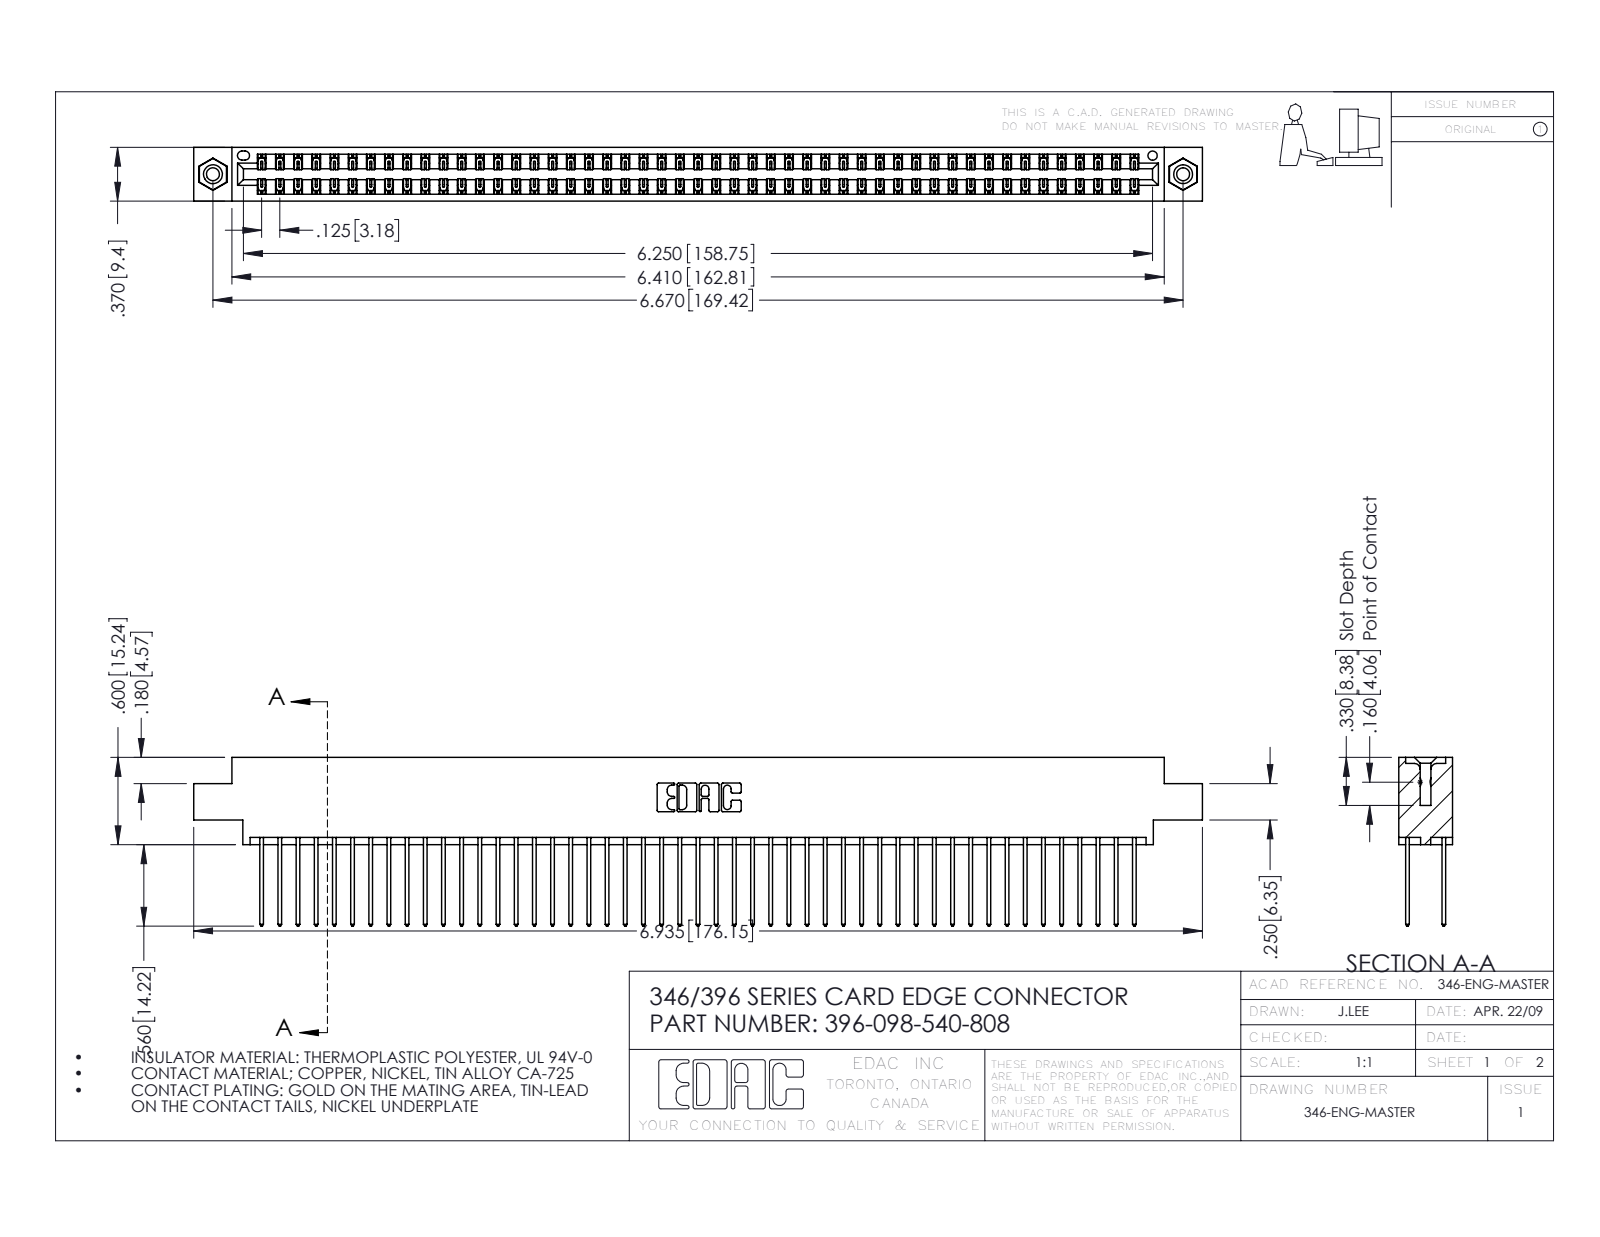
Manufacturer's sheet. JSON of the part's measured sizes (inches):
{"part_name": "346 Part_0.170 Offset - 0.156 Dia-TI; 396-098-540-808; 345-250-001_345-250-003-102; 345-292-001_345-293-140", "step_written_by": "SolidWorks 2016 (CONFIG_CONTROL_DESIGN)", "units": "inches", "bodies": {"solids": 101, "faces": 5282, "planar": 3542, "cylindrical": 1724, "other": 16}, "overall_size": [6.935, 1.16, 0.37], "volume_in3": 1.064, "surface_area_in2": 40.36, "round_holes": [[0.089, 2], [0.125, 2], [0.156, 2], [0.064, 1]], "round_bosses_or_shafts": [[0.155, 2]], "partial_cylinders_radius": [[0.006, 147], [0.01, 98], [0.01, 22], [0.007, 6], [0.031, 6], [0.026, 3], [0.014, 2], [0.022, 2]], "face_to_face_distances": [0.048, 0.322, 0.25, 0.072, 0.298, 0.025, 0.37, 0.275, 0.222, 0.148], "hole_center_spacings": [0.246, 6.461, 6.67]}
